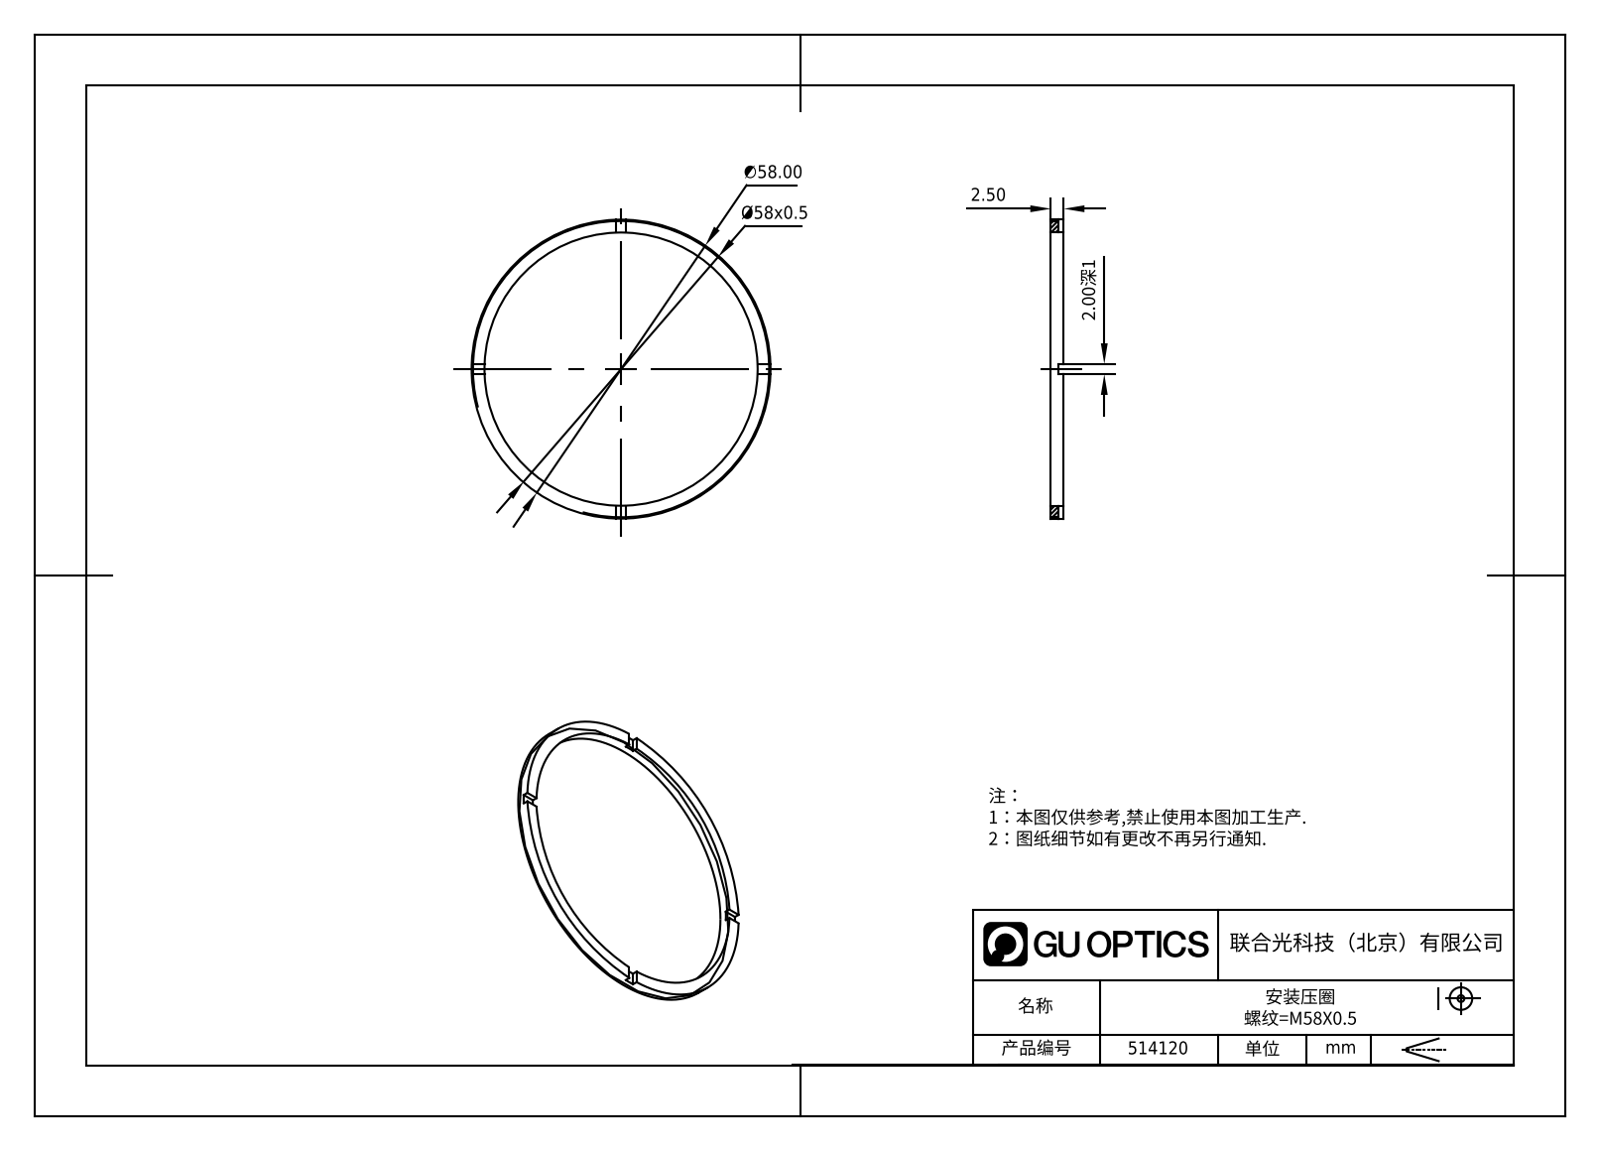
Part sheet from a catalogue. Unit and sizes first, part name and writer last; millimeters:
Units: millimetres
Overall size (bounding box): 58 × 58 × 2.5
Round holes (diameter × count): ⌀53 ×1
Round bosses / shafts (diameter × count): ⌀58 ×1
Main face-to-face distances: 2.5, 1.5, 1, 2
Volume: 1 070 mm³ · Surface area: 1 748 mm²
Bodies: 1 solid, 21 faces (17 planar, 4 cylindrical, 0 other)
Part name (STEP PRODUCT): 514120
STEP written by: SolidWorks 2020 (CONFIG_CONTROL_DESIGN)
